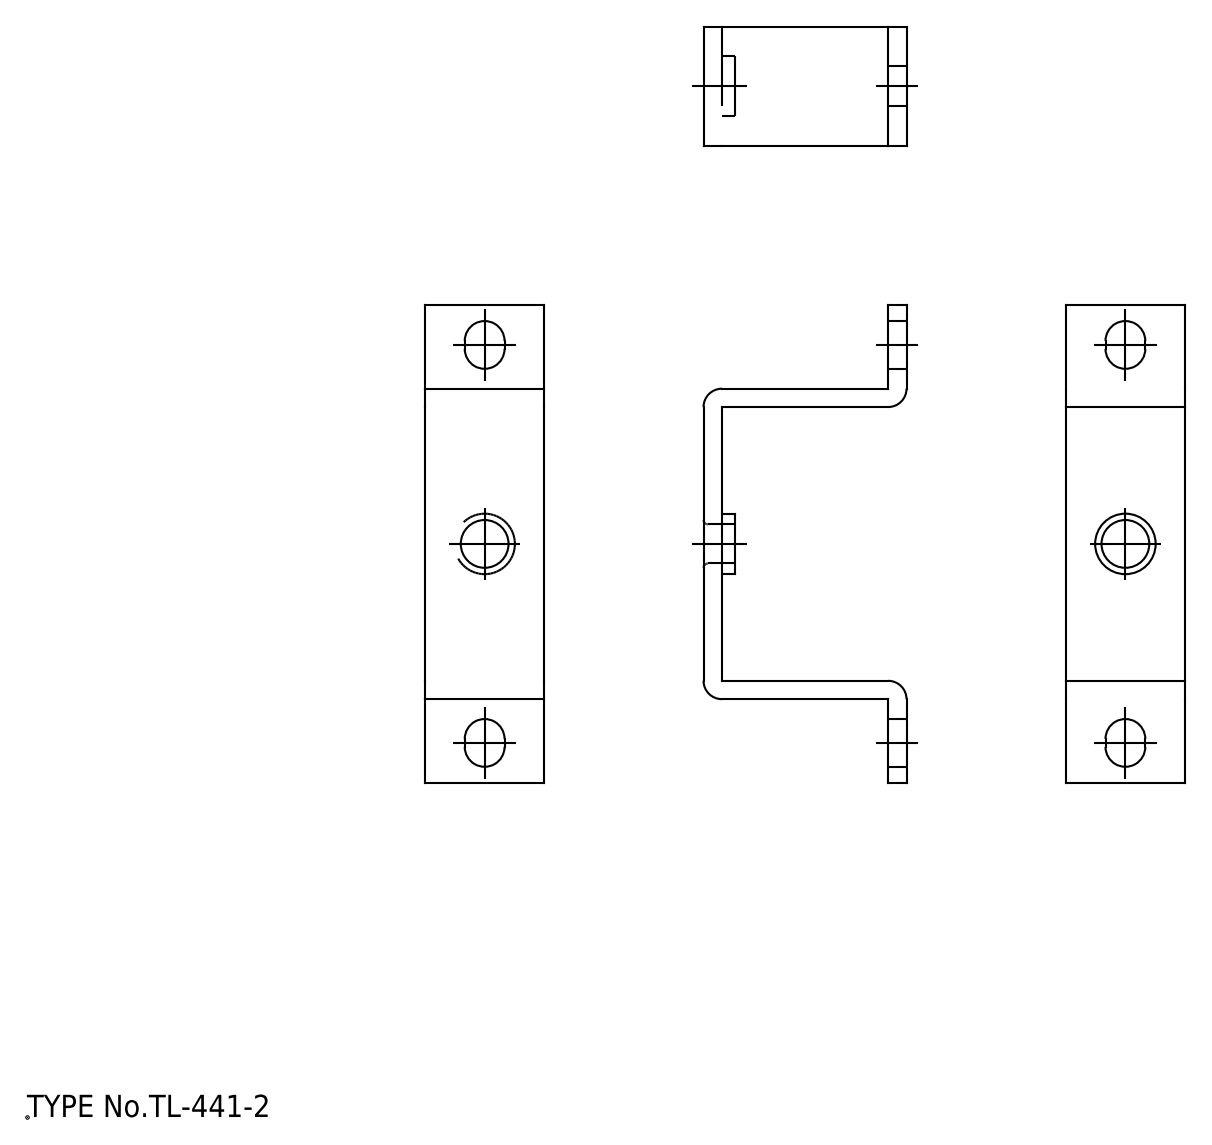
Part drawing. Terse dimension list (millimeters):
written by: spGate 19.8.4 (****-****-****-****) (AUTOMOTIVE_DESIGN)
unit: mm
bodies: 1 solid, 33 faces (19 planar, 12 cylindrical, 2 other)
size: 60 × 25.5 × 15
volume: 3 452 mm³; area: 3 721 mm²
holes: 1× ⌀6
bosses: 1× ⌀7.6
rounds: 4× R2.3, 4× R2.5
face distances: 2.3, 36.7, 23.2, 39, 34.4, 20.9, 25.5, 15, 10.5, 12.8
